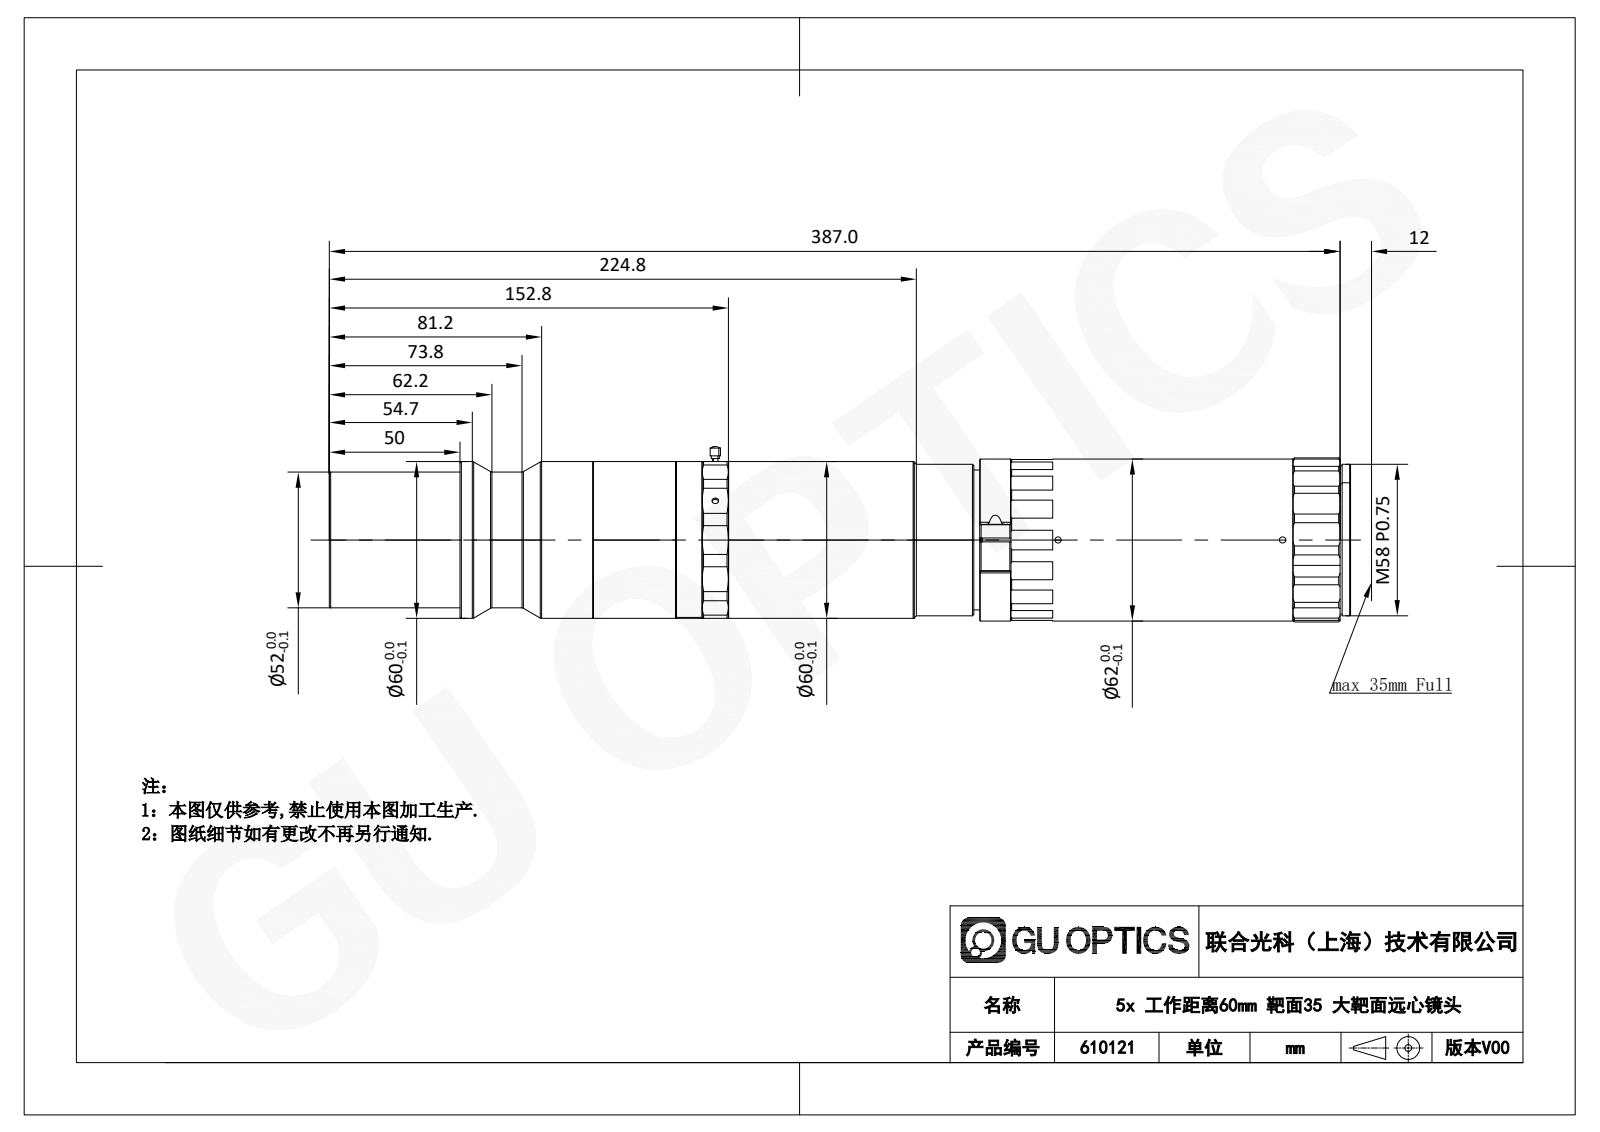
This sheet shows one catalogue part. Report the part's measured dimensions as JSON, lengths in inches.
{"part_name": "DTCA35F-8.8-G-M58-AL", "step_written_by": "SolidWorks 2017 (CONFIG_CONTROL_DESIGN)", "units": "inches", "bodies": {"solids": 1, "faces": 451, "planar": 126, "cylindrical": 165, "other": 160}, "overall_size": [15.394, 2.713, 2.645], "volume_in3": 65.66, "surface_area_in2": 128.5, "round_holes": [[0.094, 6], [0.098, 3], [0.087, 1], [0.134, 1], [0.177, 1], [1.831, 1], [2.295, 1]], "round_bosses_or_shafts": [[2.441, 1], [2.362, 1], [2.284, 1], [2.283, 1], [2.244, 1], [2.236, 1], [2.106, 1], [2.047, 1]], "partial_cylinders_radius": [[0.591, 32], [0.039, 2], [0.157, 1], [1.114, 1], [1.201, 1], [1.24, 1], [1.476, 1]], "face_to_face_distances": [5.591, 2.362, 7.835, 13.426, 13.268, 5.433, 0.157, 5.679, 7.747, 0.088], "hole_center_spacings": [3.386, 4.423]}
